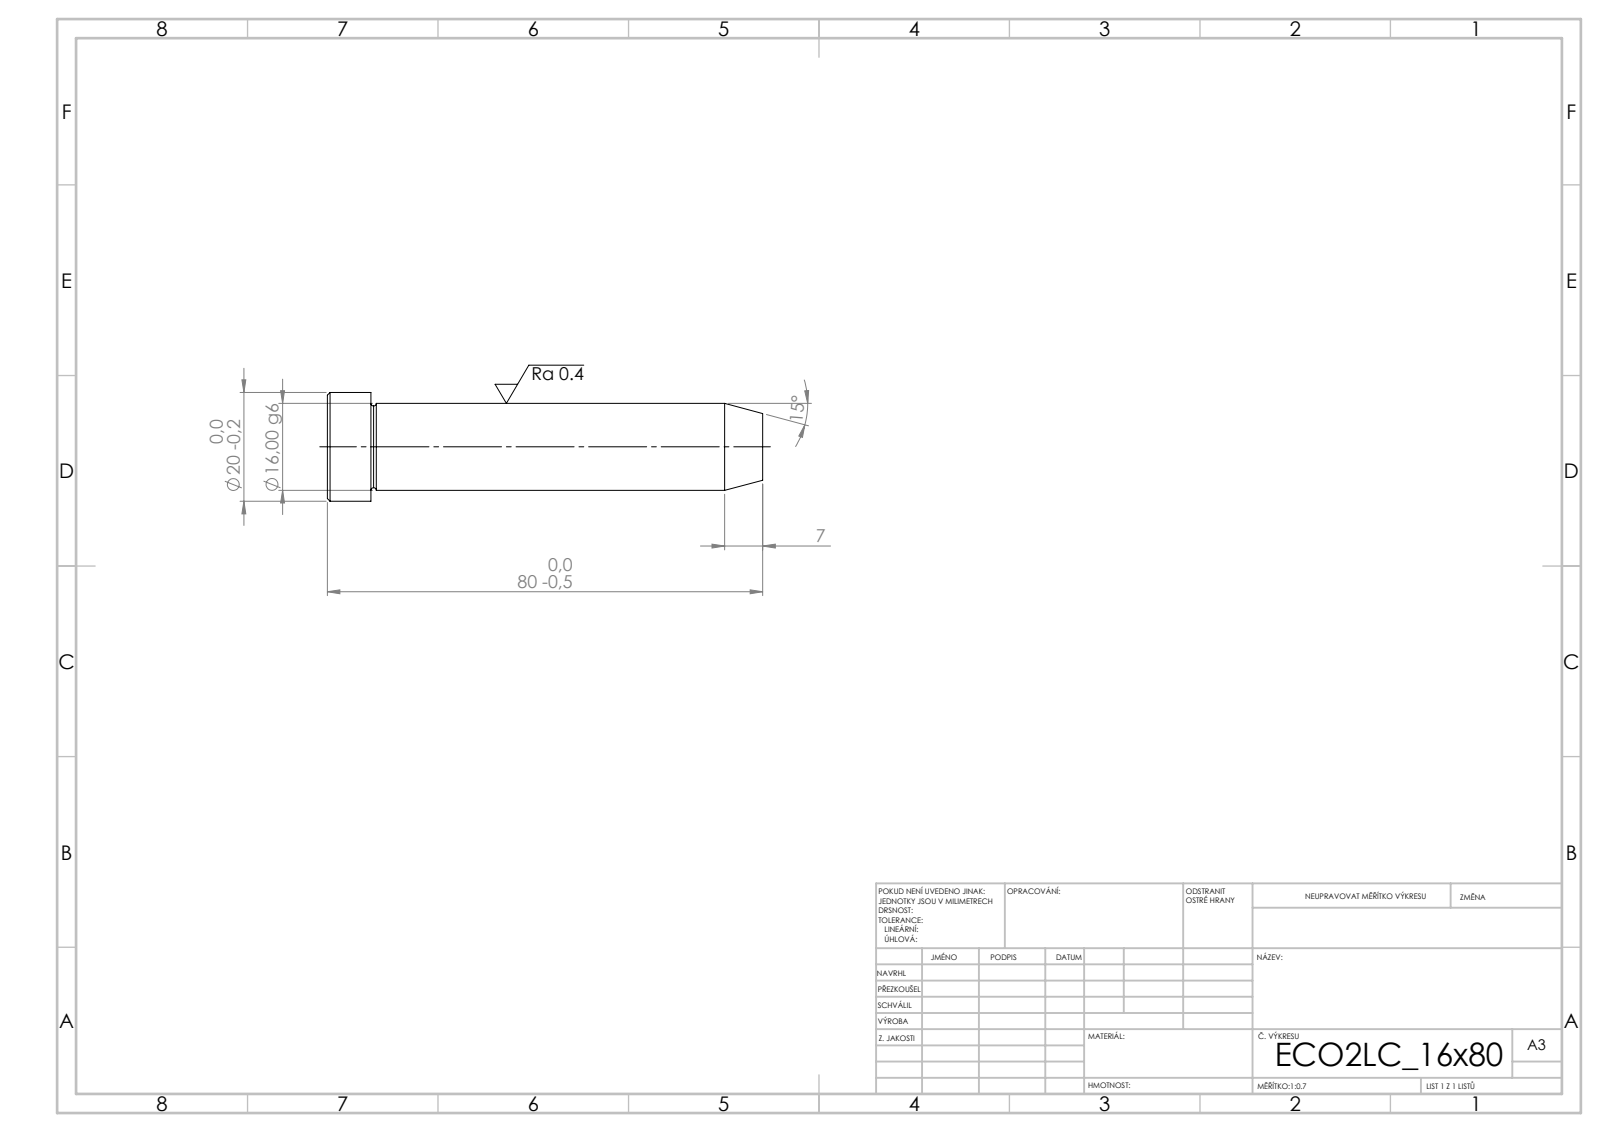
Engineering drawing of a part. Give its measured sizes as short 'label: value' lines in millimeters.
written by: SolidWorks 2019 (CONFIG_CONTROL_DESIGN)
unit: mm
bodies: 1 solid, 15 faces (3 planar, 4 cylindrical, 8 other)
size: 80 × 20 × 20
volume: 16 659 mm³; area: 4 643 mm²
bosses: 1× ⌀20, 1× ⌀16
face distances: 80, 72, 8
